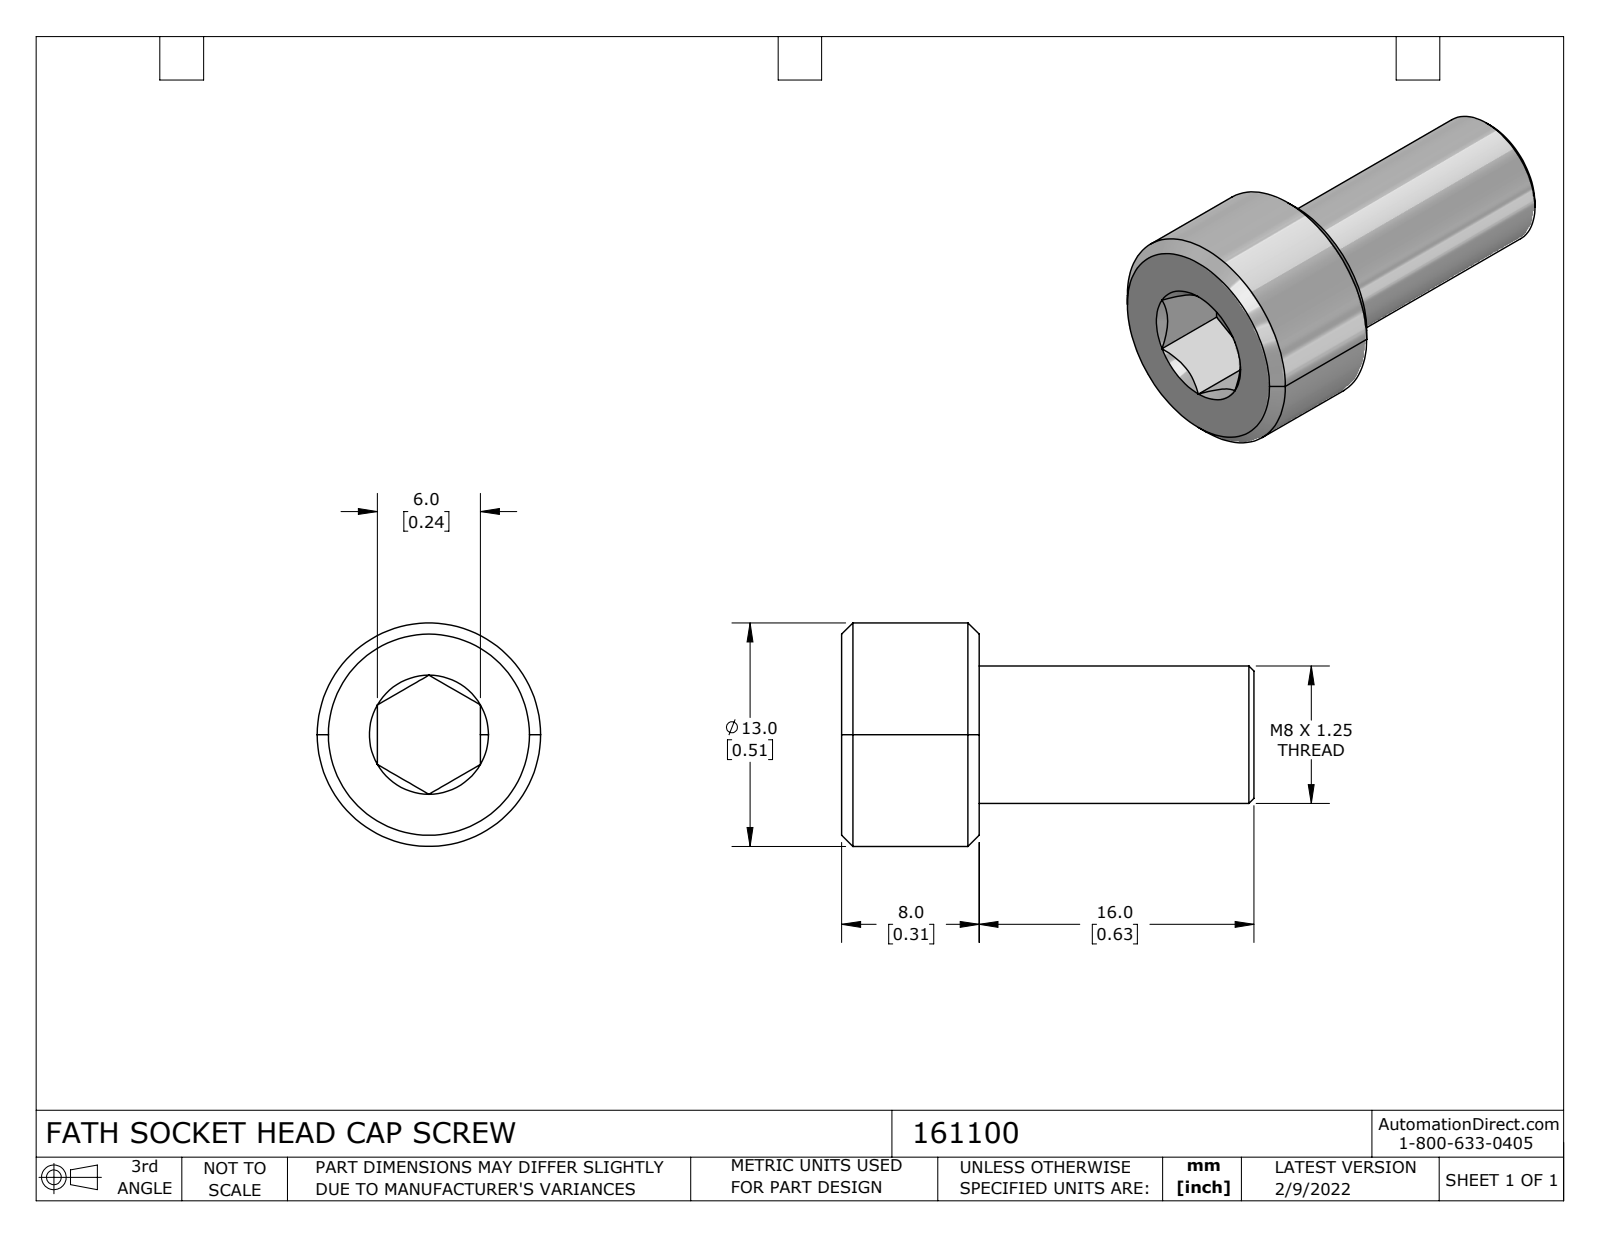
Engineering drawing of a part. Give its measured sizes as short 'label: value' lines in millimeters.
name: 161100
written by: SolidWorks 2021 (CONFIG_CONTROL_DESIGN)
unit: mm
bodies: 1 solid, 27 faces (10 planar, 4 cylindrical, 13 other)
size: 24 × 13 × 13
volume: 1 707 mm³; area: 1 048 mm²
bosses: 1× ⌀13, 1× ⌀8
face distances: 8, 6, 24, 16, 4.5, 3.5, 19.5
